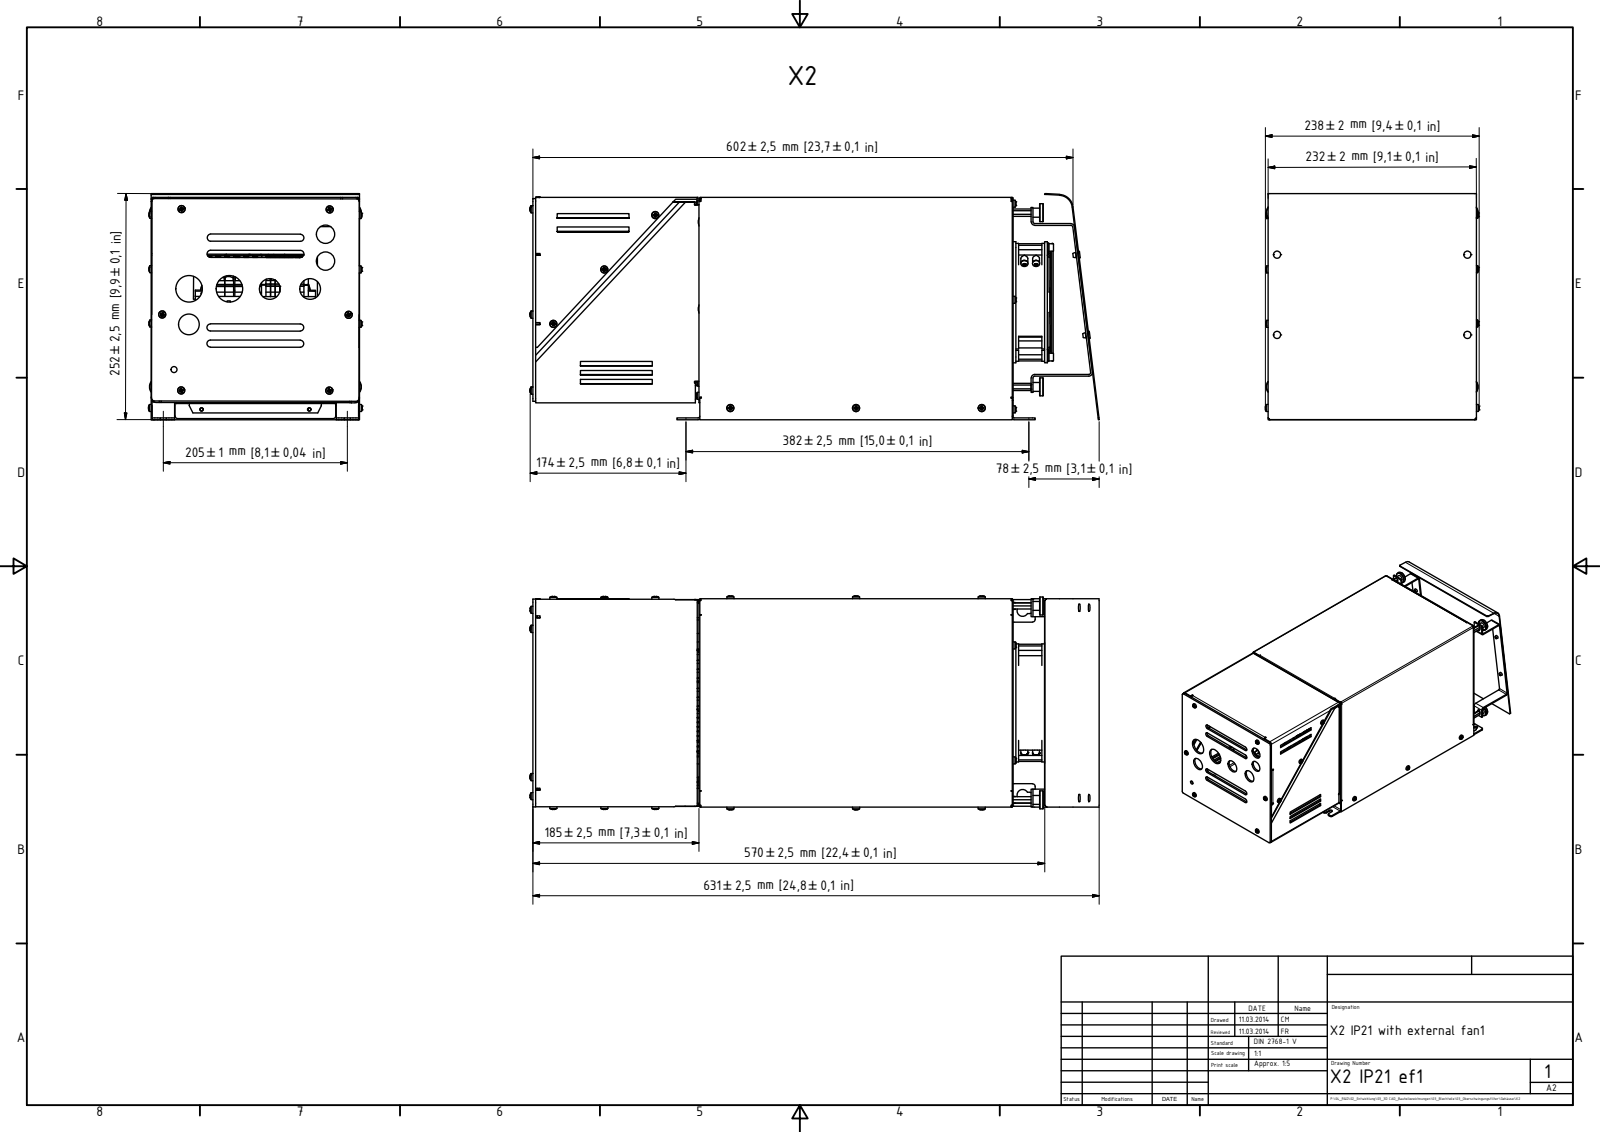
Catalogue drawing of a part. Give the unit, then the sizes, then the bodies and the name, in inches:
Units: inches
Overall size (bounding box): 24.956 × 9.914 × 9.379
Round holes (diameter × count): ⌀0.128 ×29, ⌀0.197 ×25, ⌀0.157 ×24, ⌀0.249 ×12, ⌀0.256 ×11, ⌀0.236 ×10, ⌀0.138 ×8, ⌀0.217 ×8, ⌀0.165 ×7, ⌀0.163 ×6, ⌀0.209 ×6, ⌀0.213 ×6
Round bosses / shafts (diameter × count): ⌀0.157 ×36, ⌀0.059 ×24, ⌀0.144 ×23, ⌀0.394 ×10, ⌀0.197 ×10, ⌀0.362 ×8, ⌀0.335 ×6, ⌀0.787 ×4
Partial cylindrical surfaces — rounded edges, fillets, slot ends (radius × count): R0.02 ×159, R0.03 ×75, R0.079 ×74, R0.006 ×44, R0.118 ×40, R0.004 ×32, R0.008 ×31, R0.039 ×31
Main face-to-face distances: 0.039, 0.079, 9.094, 9.055, 13.738, 9.134, 8.957, 0.118, 8.996, 9.035
Hole centre spacings: 0.201, 0.928, 0.402, 0.906, 0.991, 8.346, 0.602, 1.087
Volume: 93.18 in³ · Surface area: 2 868 in²
Bodies: 127 solids, 8293 faces (5129 planar, 2171 cylindrical, 993 other)
Part name (STEP PRODUCT): 10100277 Bodenblech X2; 10100385 Deckel X2-A; 10100459 Lüfterblech X2-A; 10100384 Anschlussblech X2-A (+8 more)
STEP written by: Autodesk Inventor 2015 (AUTOMOTIVE_DESIGN)
